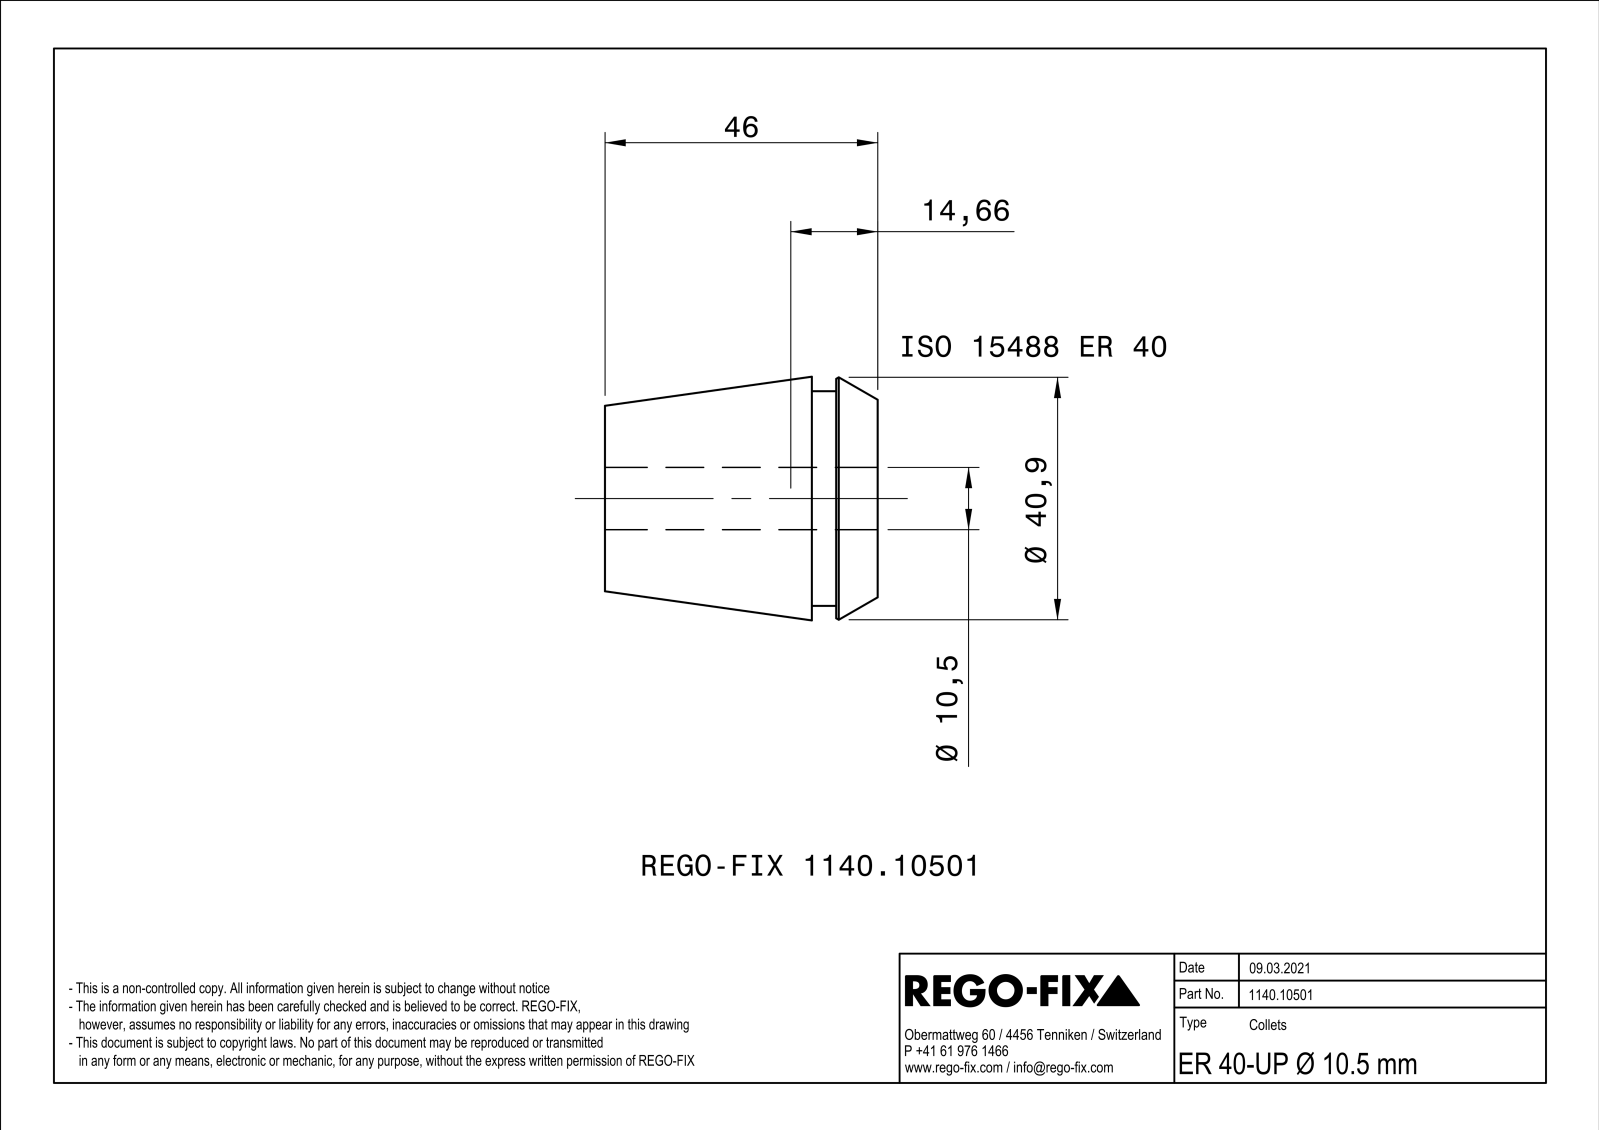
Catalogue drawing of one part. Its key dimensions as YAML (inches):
part_name: "NOCUT"
step_written_by: "SIEMENS PLM Software Solid Edge ST10 (AUTOMOTIVE_DESIGN)"
units: inches
bodies: {solids: 1, faces: 177, planar: 88, cylindrical: 9, other: 80}
overall_size: [1.811, 1.614, 1.614]
volume: 2.164
surface_area: 37.74
round_holes:
  - {diameter: 0.413, count: 1}
round_bosses_or_shafts:
  - {diameter: 1.425, count: 1}
face_to_face_distances: [0.039, 1.811, 0.437, 1.374, 0.276, 0.161, 1.535, 0.295, 0.02, 0.142]
